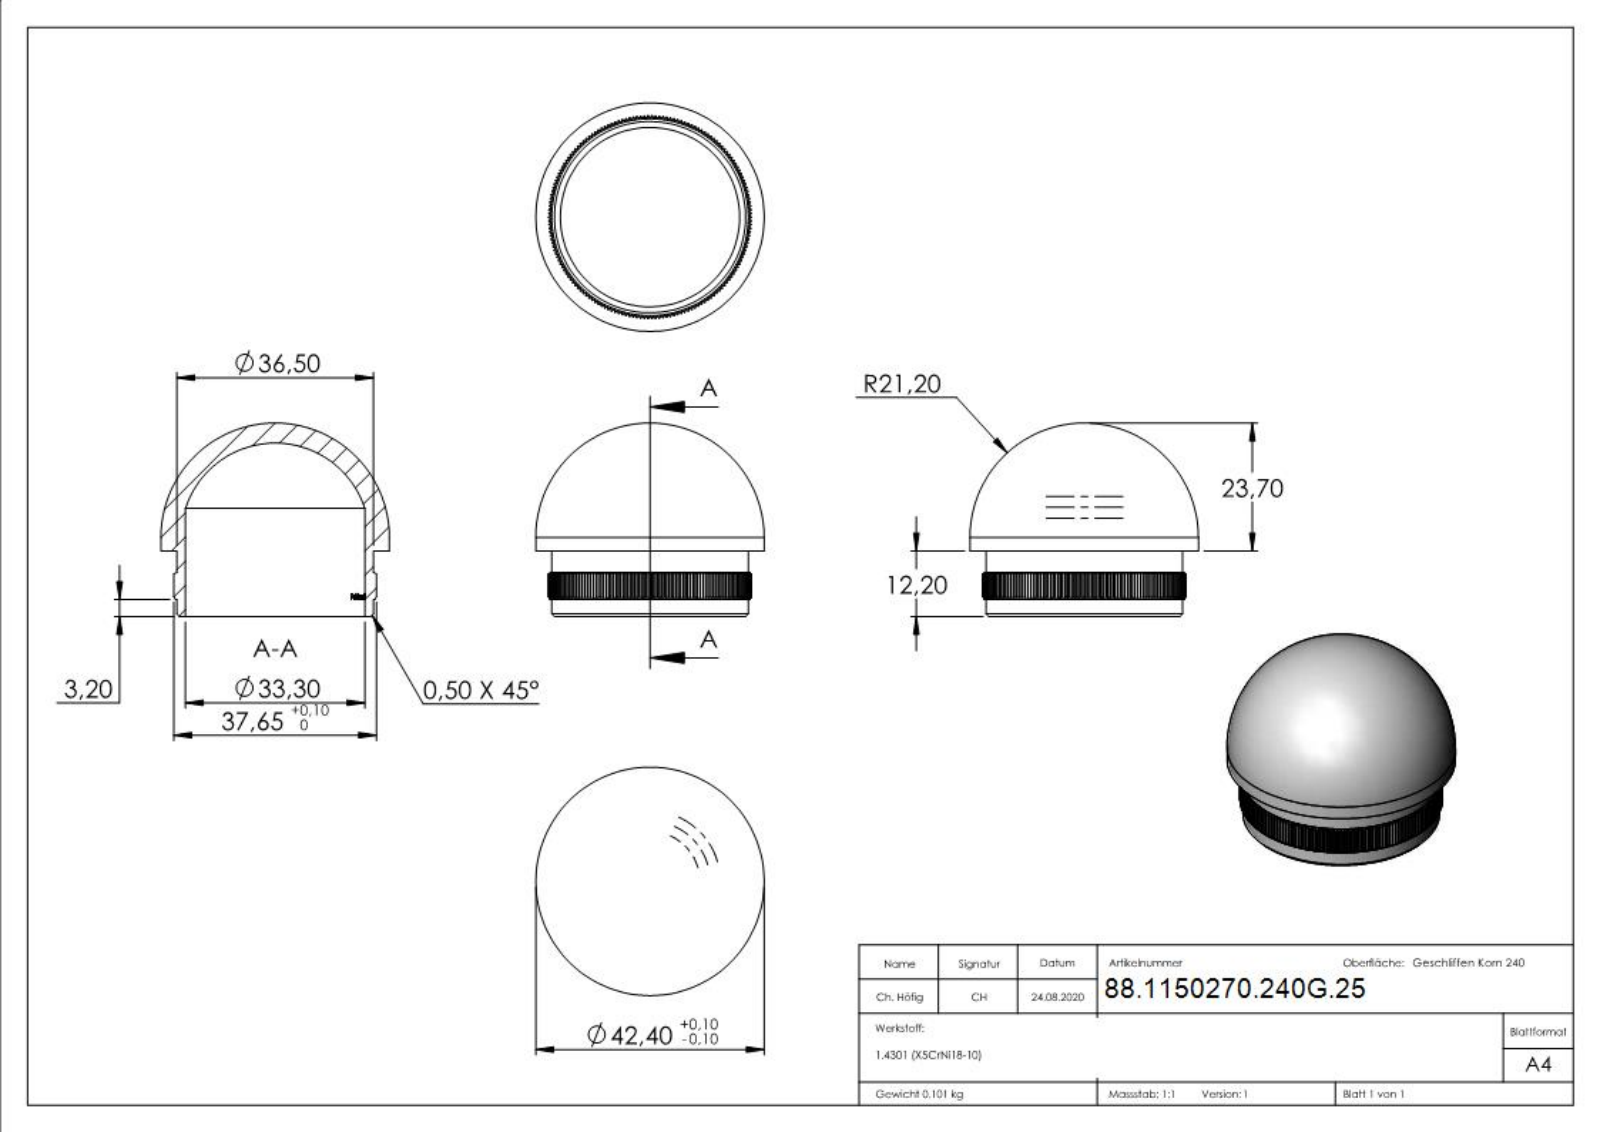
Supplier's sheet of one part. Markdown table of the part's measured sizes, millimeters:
| quantity | value |
| --- | --- |
| part name | 50270-240G-25 |
| STEP written by | SolidWorks 2018 (CONFIG_CONTROL_DESIGN) |
| units | millimeters |
| bodies | 1 solid, 1122 faces (459 planar, 202 cylindrical, 461 other) |
| overall size | 42.4 × 42.4 × 35.9 |
| volume | 12 744 mm³ |
| surface area | 9 044 mm² |
| round holes (diameter × count) | 33.3 × 1 |
| round bosses / shafts (diameter × count) | 42.4 × 1, 36.5 × 1 |
| partial cylindrical surfaces (radius × count) | 16.75 × 1, 18.82 × 1 |
| main face-to-face distances | 18.32, 18.34, 12.2, 3.2, 9, 18.3, 8.2, 5, 4, 0.95 |
